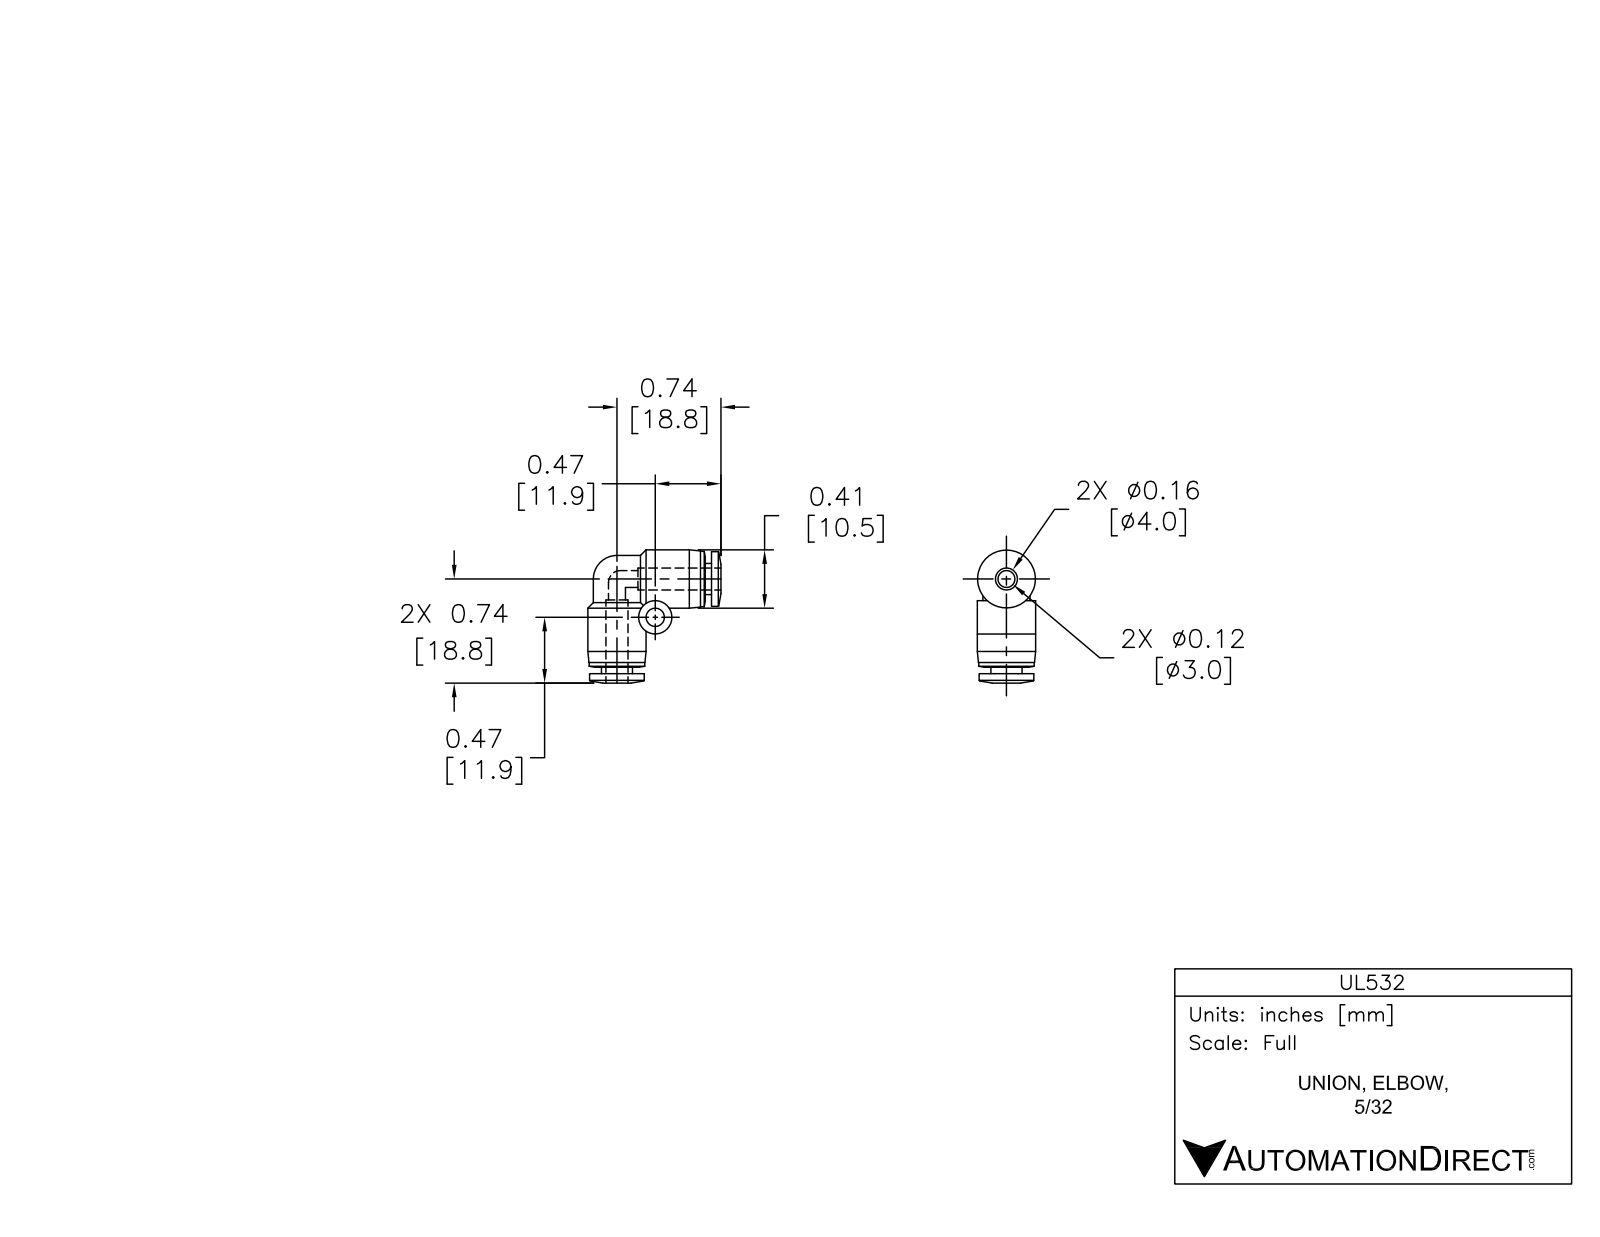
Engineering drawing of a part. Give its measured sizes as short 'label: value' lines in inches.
name: UL532
written by: SolidWorks 2015 (AUTOMOTIVE_DESIGN)
unit: in
bodies: 1 solid, 74 faces (10 planar, 32 cylindrical, 32 other)
size: 0.945 × 0.945 × 0.413
volume: 0.145 in³; area: 3.338 in²
holes: 2× ⌀0.134, 2× ⌀0.169, 1× ⌀0.13
bosses: 2× ⌀0.413, 2× ⌀0.394, 2× ⌀0.388, 2× ⌀0.335, 2× ⌀0.22, 1× ⌀0.236
face distances: 0.045, 0.413, 0.47, 0.516, 0.437, 0.033, 0.079
